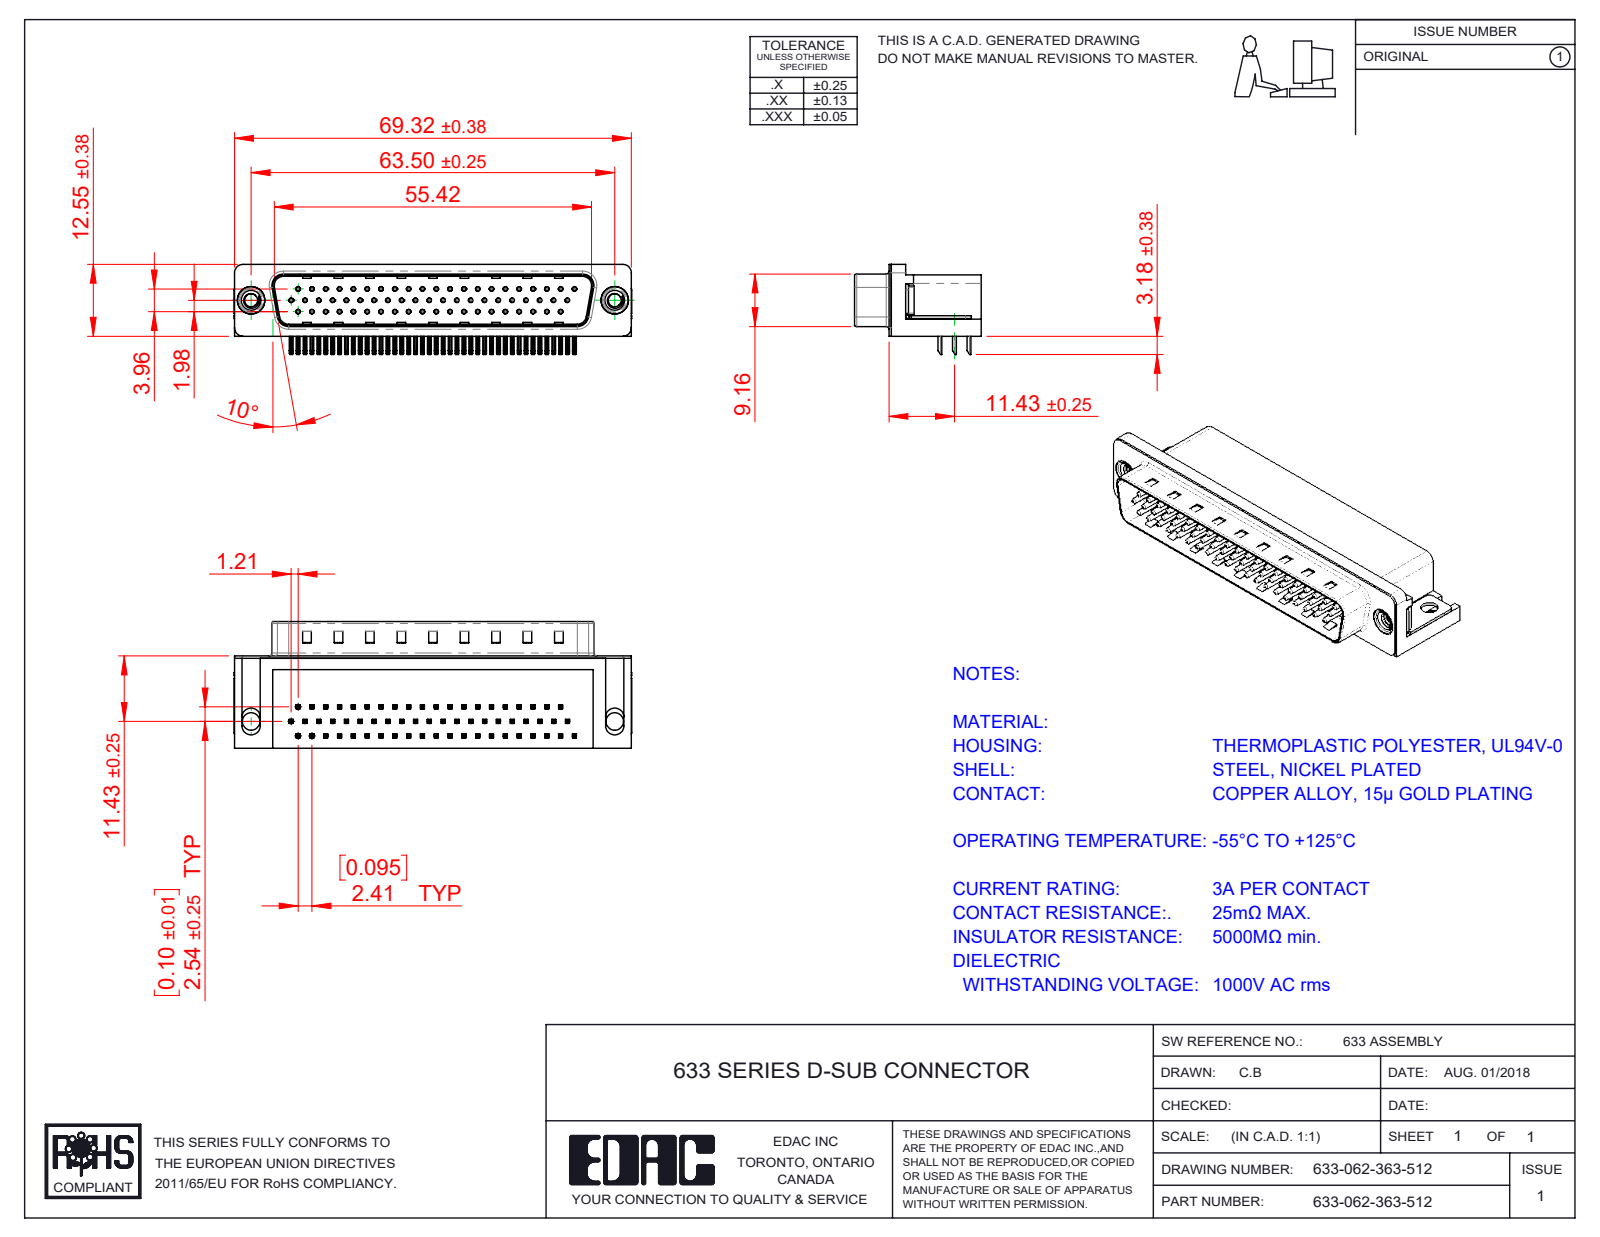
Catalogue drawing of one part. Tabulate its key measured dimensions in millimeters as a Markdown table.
| quantity | value |
| --- | --- |
| part name | 633 Housing_62 Contact; 633 Contact Top; 633 4-40 Threaded Rivet; 633 Shell_62 Contact (+4 more) |
| STEP written by | SolidWorks 2016 (CONFIG_CONTROL_DESIGN) |
| units | millimeters |
| bodies | 68 solids, 5074 faces (3211 planar, 1442 cylindrical, 421 other) |
| overall size | 69.4 × 22.1 × 15.73 |
| volume | 11 054 mm³ |
| surface area | 13 393 mm² |
| round holes (diameter × count) | 0.35 × 62, 0.8 × 62, 2.26 × 2, 3.05 × 2, 4 × 2, 4.8 × 2, 5 × 2 |
| round bosses / shafts (diameter × count) | 0.75 × 62, 4.9 × 2, 4.75 × 2, 3.9 × 2 |
| partial cylindrical surfaces (radius × count) | 0.25 × 256, 0.12 × 124, 1 × 16, 0.5 × 9, 1.6 × 8, 1.5 × 7, 0.9 × 4, 2 × 4 |
| main face-to-face distances | 0.4, 10.35, 15.7, 8.76, 2.9, 2.5, 2.54, 8.36, 2.1, 16.1 |
| hole center spacings | 2.41, 4.82, 7.24, 9.65, 14.48, 16.89, 4.83, 7.23 |
